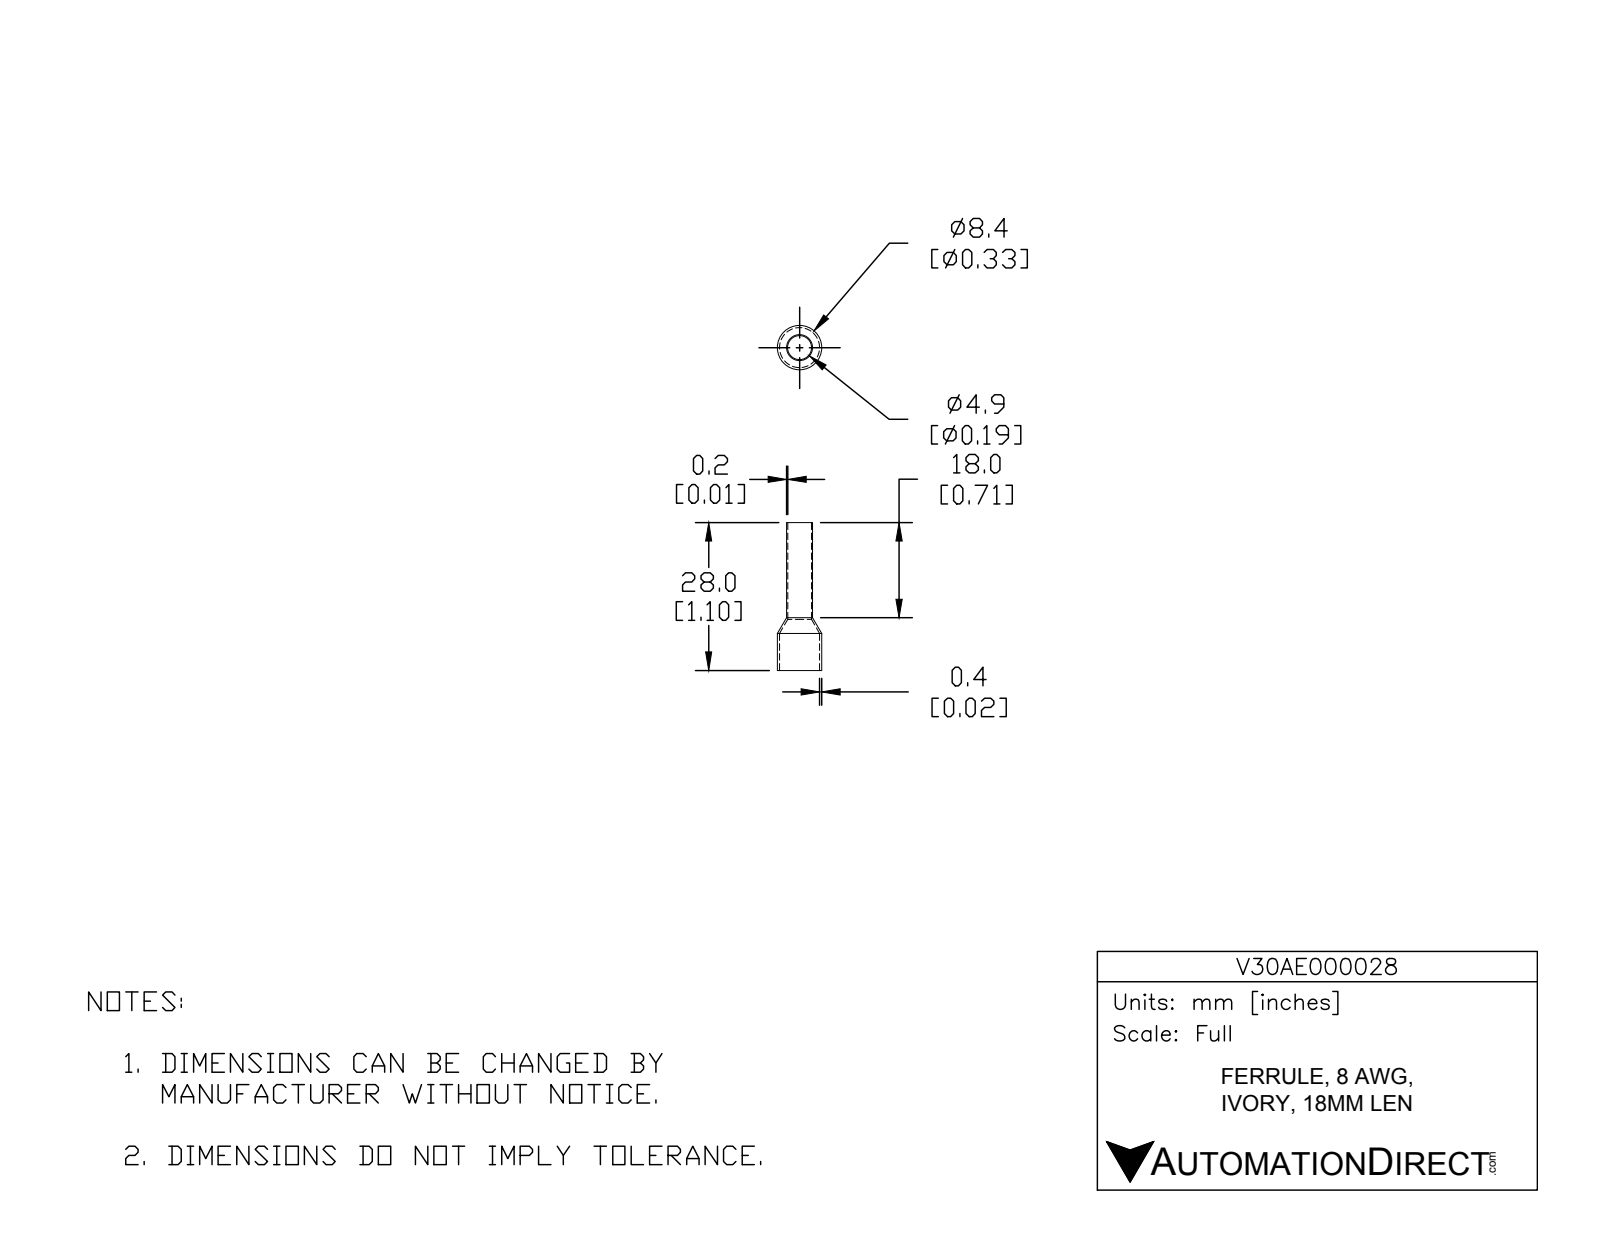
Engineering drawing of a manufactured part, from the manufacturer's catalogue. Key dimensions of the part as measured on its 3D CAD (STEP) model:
Part name (STEP PRODUCT): V30AE000028
STEP written by: SolidWorks 2017 (AUTOMOTIVE_DESIGN)
Units: millimetres
Bodies: 1 solid, 14 faces (2 planar, 8 cylindrical, 4 other)
Overall size (bounding box): 28 × 8.4 × 8.4
Volume: 147 mm³ · Surface area: 1 032 mm²
Round holes (diameter × count): ⌀4.5 ×1, ⌀7.6 ×1
Round bosses / shafts (diameter × count): ⌀8.4 ×1, ⌀4.9 ×1
Main face-to-face distances: 28
